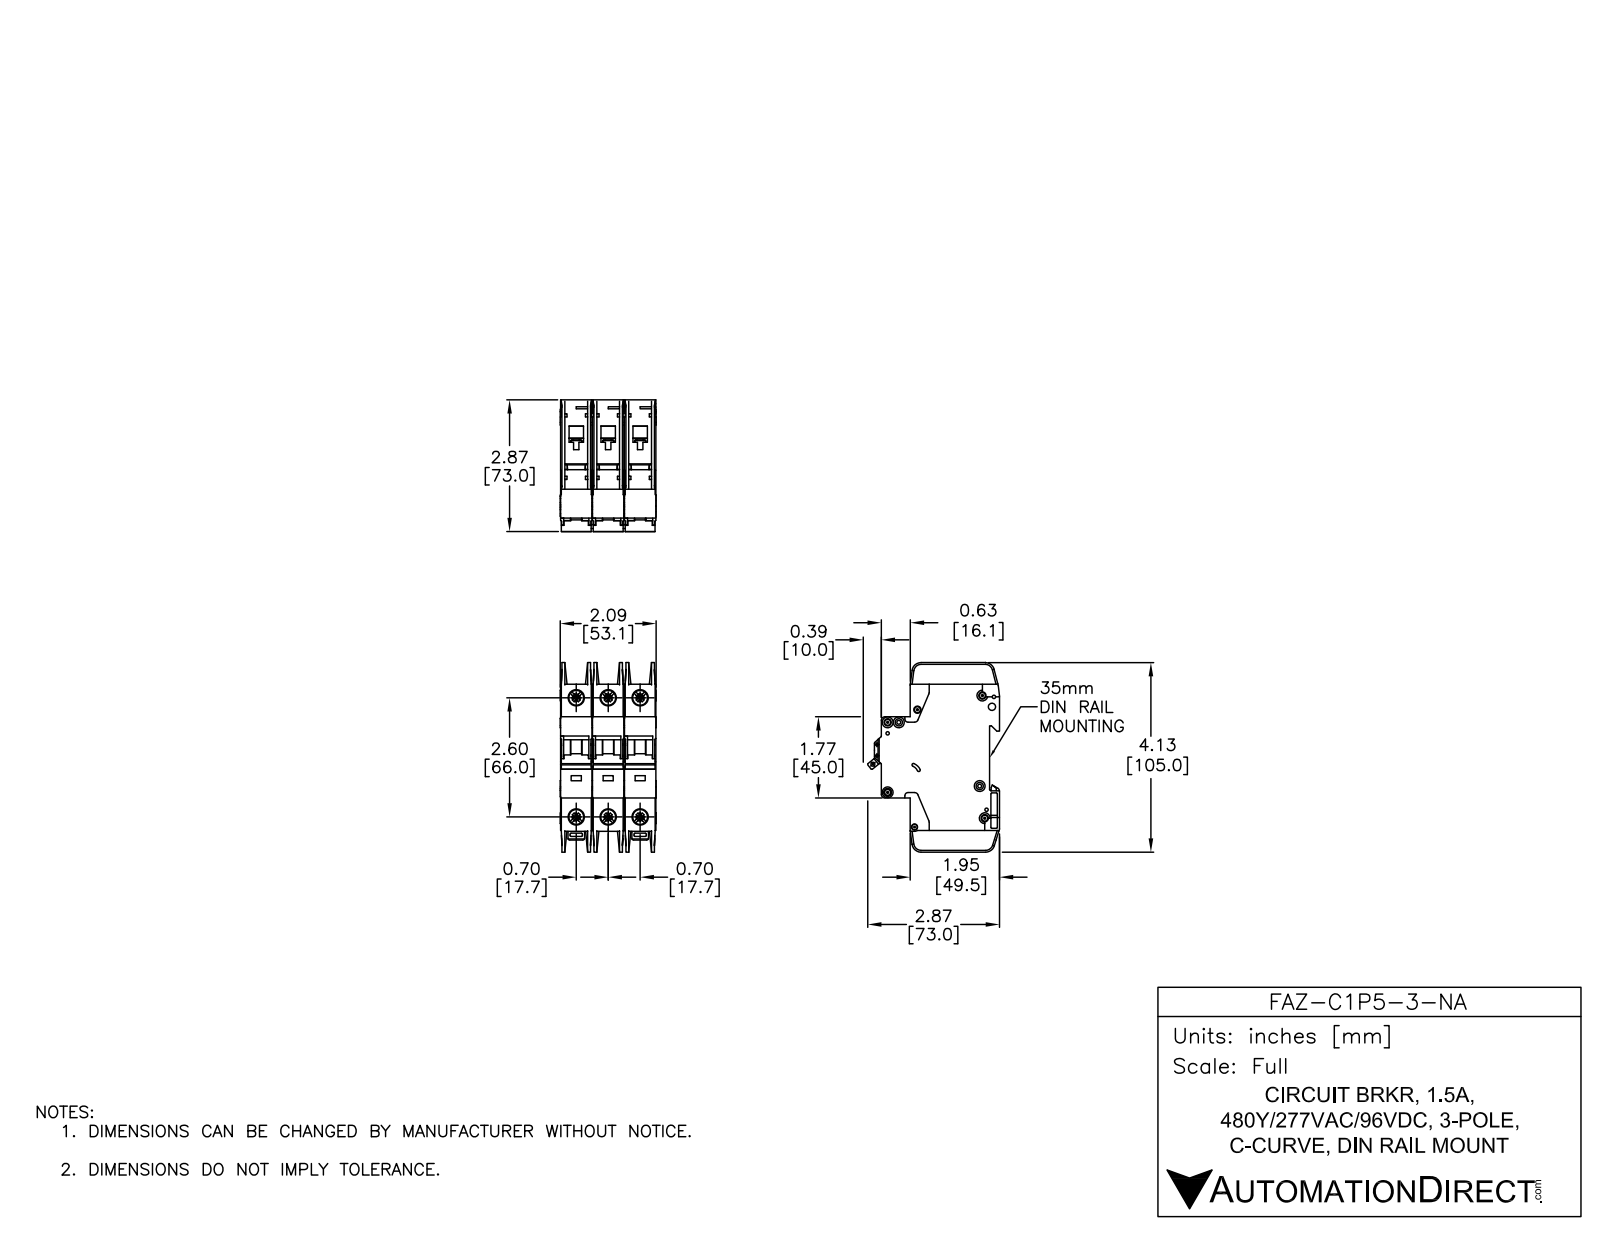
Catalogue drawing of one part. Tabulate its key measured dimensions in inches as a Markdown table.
| quantity | value |
| --- | --- |
| part name | FAZ-C1P5-3-NA |
| STEP written by | SolidWorks 2014 (AUTOMOTIVE_DESIGN) |
| units | inches |
| bodies | 9 solids, 2352 faces (1227 planar, 789 cylindrical, 336 other) |
| overall size | 4.134 × 2.876 × 2.091 |
| volume | 14.22 in³ |
| surface area | 115 in² |
| round holes (diameter × count) | 0.142 × 7, 0.281 × 6, 0.323 × 6, 0.043 × 2, 0.059 × 2, 0.157 × 2, 0.075 × 1, 0.085 × 1, 0.087 × 1, 0.1 × 1, 0.13 × 1, 0.134 × 1 |
| round bosses / shafts (diameter × count) | 0.236 × 7, 0.098 × 3 |
| partial cylindrical surfaces (radius × count) | 0.01 × 65, 0.02 × 30, 0.039 × 26, 0.079 × 14, 0.071 × 5, 0.197 × 5, 0.157 × 4, 0.008 × 2 |
| main face-to-face distances | 0.697, 1.394, 0.689, 1.386, 0.028, 0.593, 0.096, 0.069, 0.62, 0.524 |
| hole center spacings | 0.697, 2.69, 2.598, 0.244, 1.394, 2.948, 0.204, 0.24 |
